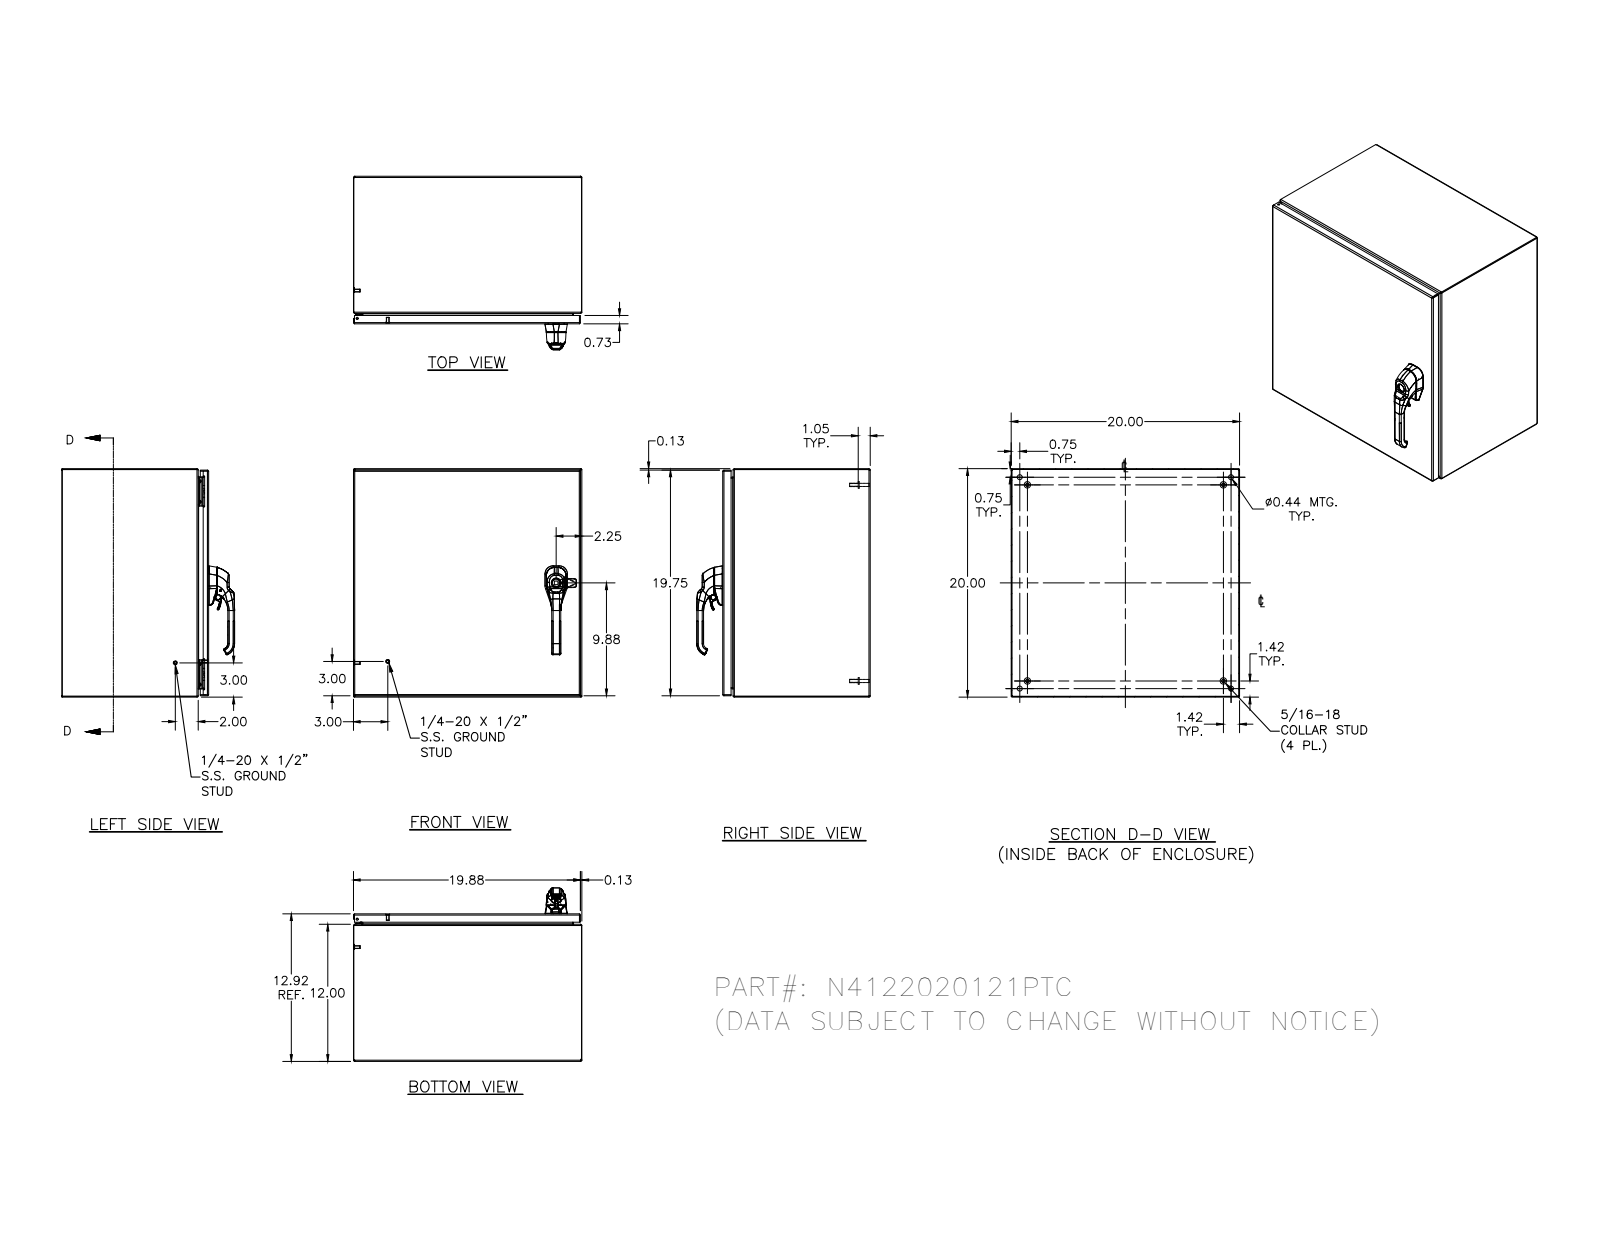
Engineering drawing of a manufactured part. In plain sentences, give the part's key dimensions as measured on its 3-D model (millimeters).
The part is named "N4122020121PTC". Its 3-D file was written by "SolidWorks 2018 (AUTOMOTIVE_DESIGN)". It is 28 solids with 1280 faces: 417 planar, 474 cylindrical and 389 other. Overall it measures 508 by 508 by 383.4 millimeters. Its volume is 2 483 000 cubic millimeters and its surface area 2 512 000 square millimeters. Round holes: 5 of diameter 4.8, 4 of diameter 2.4, 4 of diameter 3.9, 4 of diameter 4.2, 4 of diameter 4.4, 4 of diameter 11.1, 3 of diameter 7.1, 2 of diameter 4, 1 of diameter 4.7. Round bosses or shafts: 10 of diameter 6.4, 4 of diameter 14.3, 4 of diameter 9.1, 4 of diameter 8.1, 4 of diameter 7.6, 4 of diameter 7, 4 of diameter 6.5, 4 of diameter 4.2. Partial cylindrical surfaces (rounded edges, fillets, slot ends): 30 of radius 0.8, 26 of radius 1.3, 20 of radius 2.7, 18 of radius 0.4, 14 of radius 3.2, 8 of radius 0.8, 8 of radius 1.7, 8 of radius 1.7. The main face-to-face distances are 1.9, 506.1, 326.2, 508, 504.2, 328.1, 324.3, 302.9, 23.3, 487.3. The hole center spacings are 406.3, 469.9, 479.3, 0.4, 16.8, 406.5, 423.1, 0.5.
